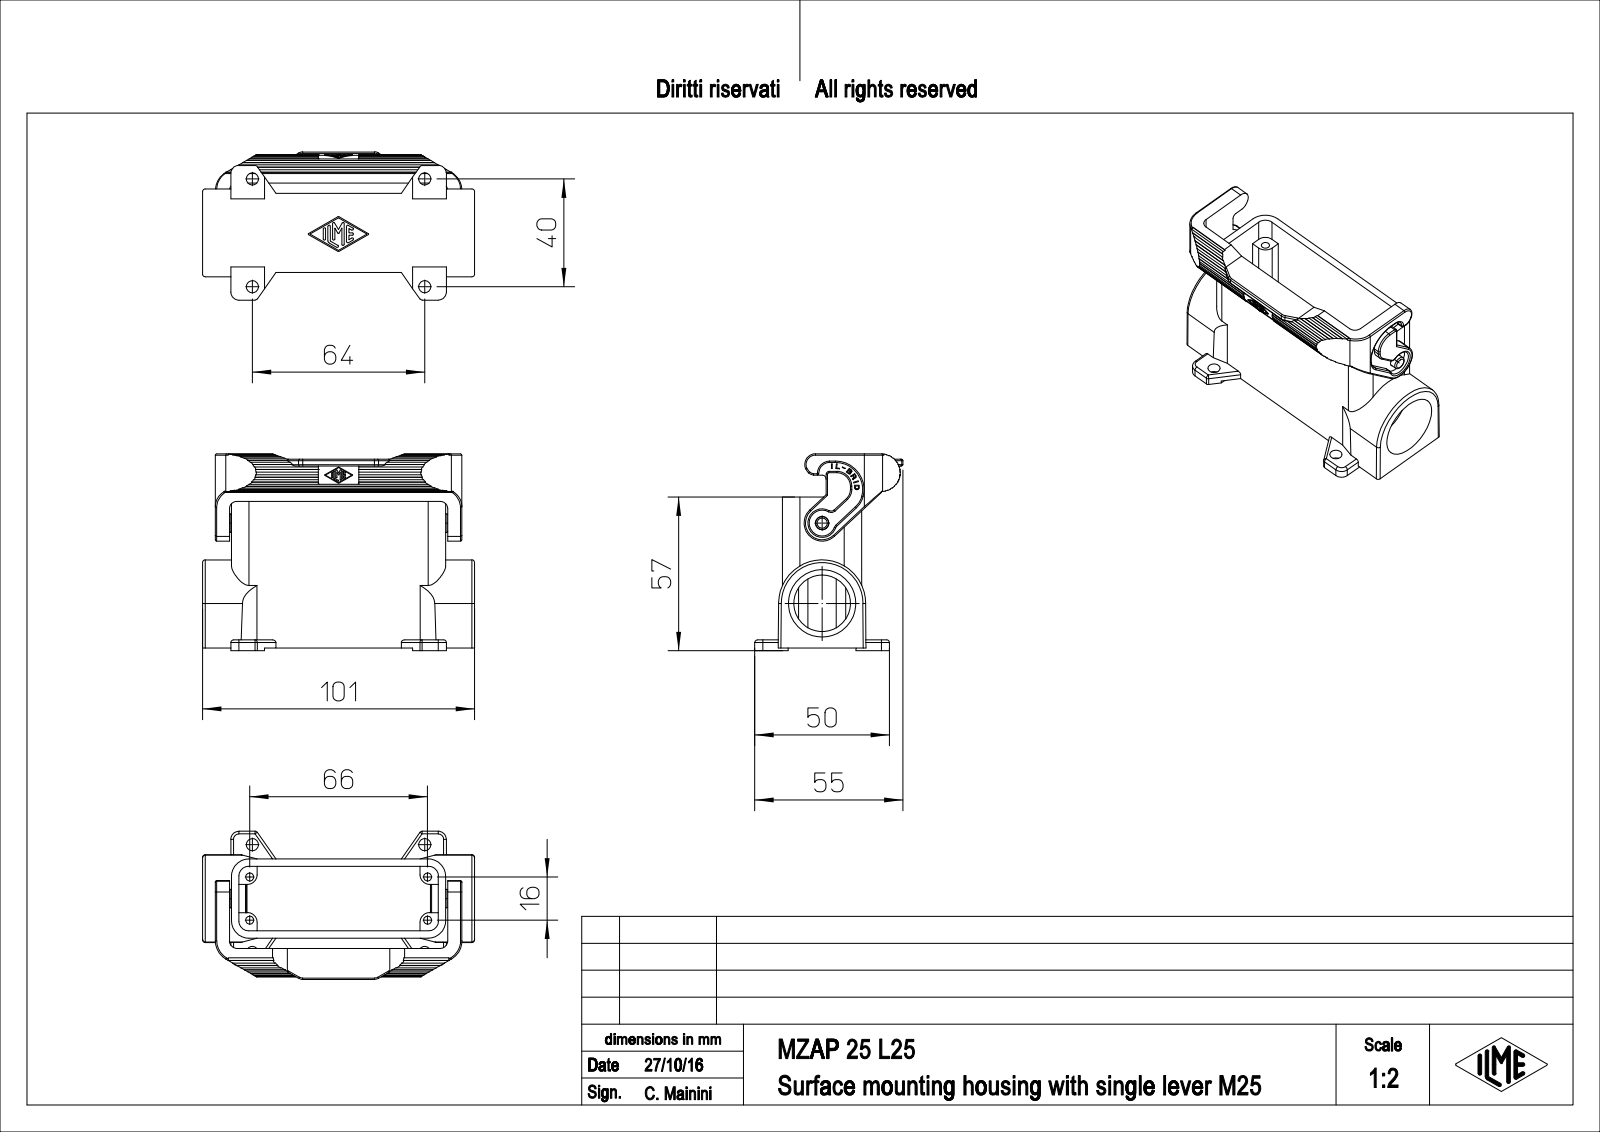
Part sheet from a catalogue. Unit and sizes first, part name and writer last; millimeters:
Units: millimetres
Overall size (bounding box): 101 × 73 × 55
Round holes (diameter × count): ⌀3 ×4, ⌀4.5 ×4, ⌀5 ×1, ⌀21 ×1, ⌀23.6 ×1, ⌀25 ×1
Round bosses / shafts (diameter × count): ⌀6.8 ×1, ⌀4.8 ×1
Partial cylindrical surfaces — rounded edges, fillets, slot ends (radius × count): R0.5 ×31, R1 ×17, R0.2 ×15, R3.5 ×8, R3 ×7, R3.2 ×4, R6.5 ×4, R0.1 ×3
Main face-to-face distances: 2.76, 26.64, 29.4, 23.88, 3, 33.2, 30.44, 6.56, 3.8, 70
Hole centre spacings: 12.04, 28.02, 66.1, 70.77, 16, 40, 64, 66
Volume: 69 775 mm³ · Surface area: 40 361 mm²
Bodies: 1 solid, 777 faces (504 planar, 215 cylindrical, 58 other)
Part name (STEP PRODUCT): MZAP_25_L25
STEP written by: PTC Creo Elements/Direct Modeling 19.0E 27-Jun-2016 (C) Parametric Technology GmbH (AUTOMOTIVE_DESIGN)
